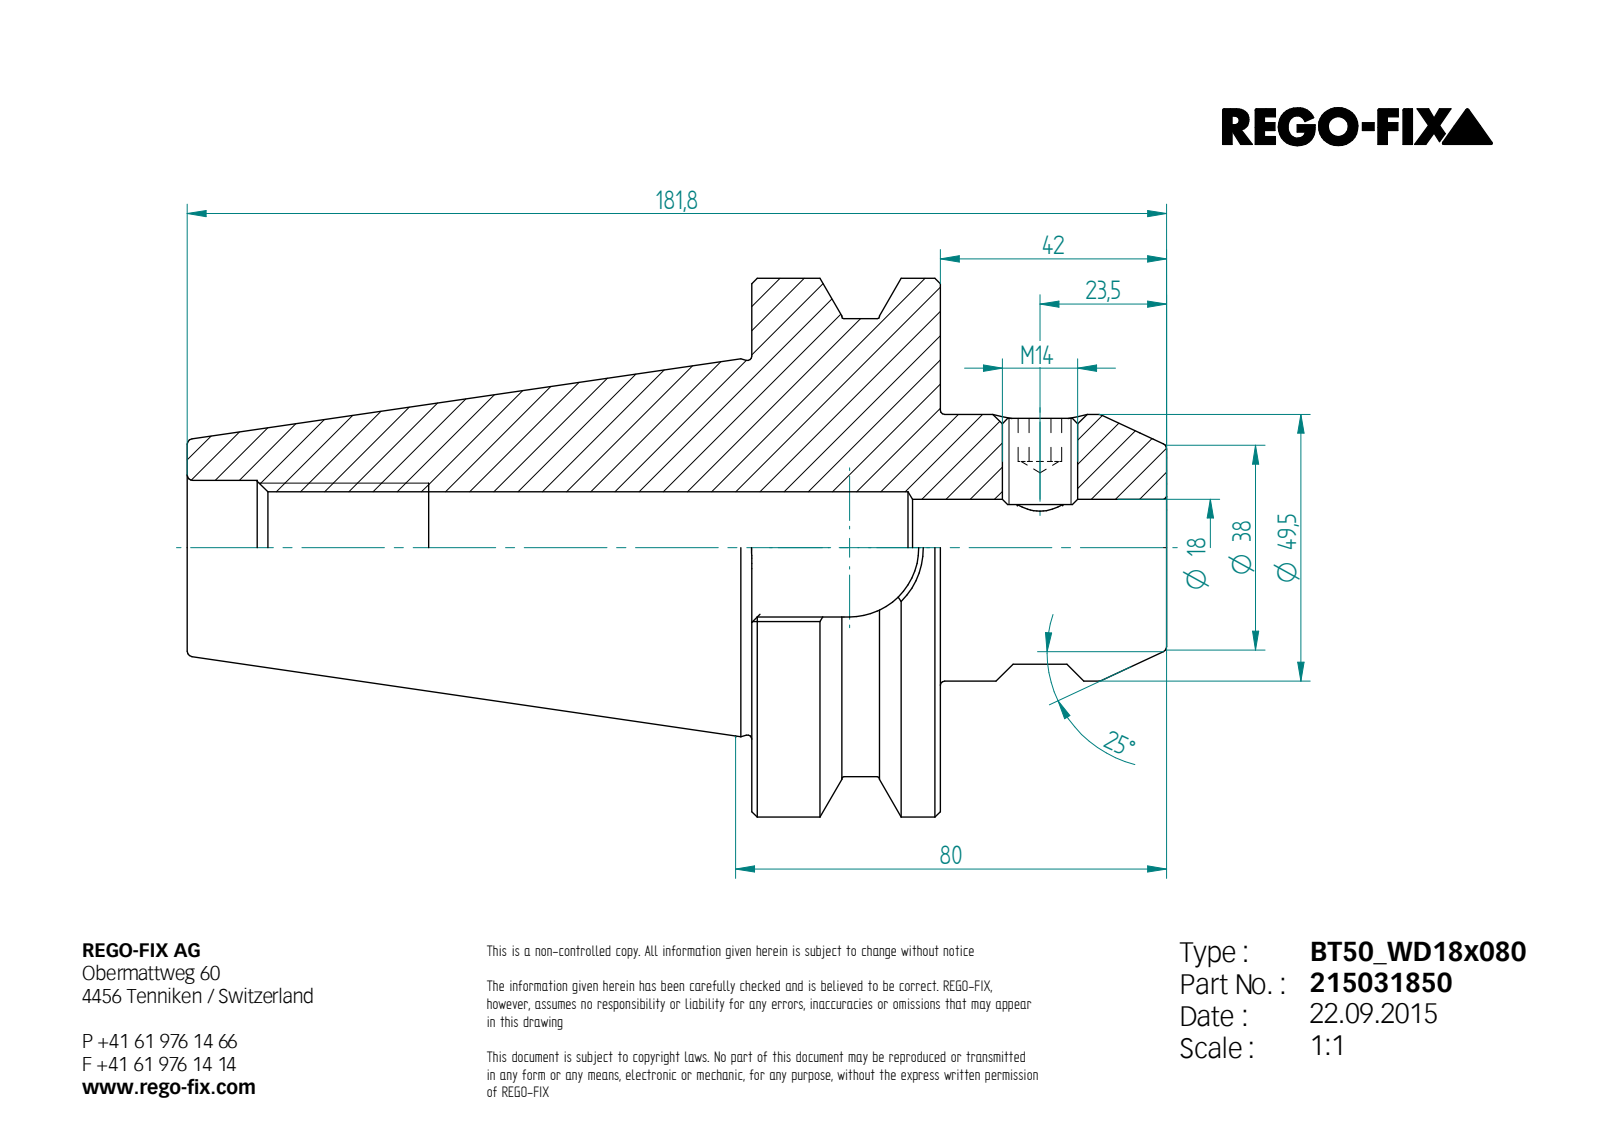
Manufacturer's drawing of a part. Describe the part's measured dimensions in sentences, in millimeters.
Its 3-D file was written by "Unknown (AUTOMOTIVE_DESIGN)". It is 2 solids with 94 faces: 45 planar, 18 cylindrical and 31 other. Overall it measures 181.8 by 100 by 100 millimeters. Its volume is 509 234 cubic millimeters and its surface area 62 727 square millimeters. Round holes: 1 of diameter 11.84, 1 of diameter 18, 1 of diameter 20.75, 1 of diameter 25. Round bosses or shafts: 1 of diameter 100, 1 of diameter 85, 1 of diameter 49.5, 1 of diameter 14. Partial cylindrical surfaces (rounded edges, fillets, slot ends): 4 of radius 0.5, 1 of radius 12.85. The main face-to-face distances are 35, 77, 42, 70.7, 104.8, 139.8, 181.8, 25.7, 8.75, 34.45.
